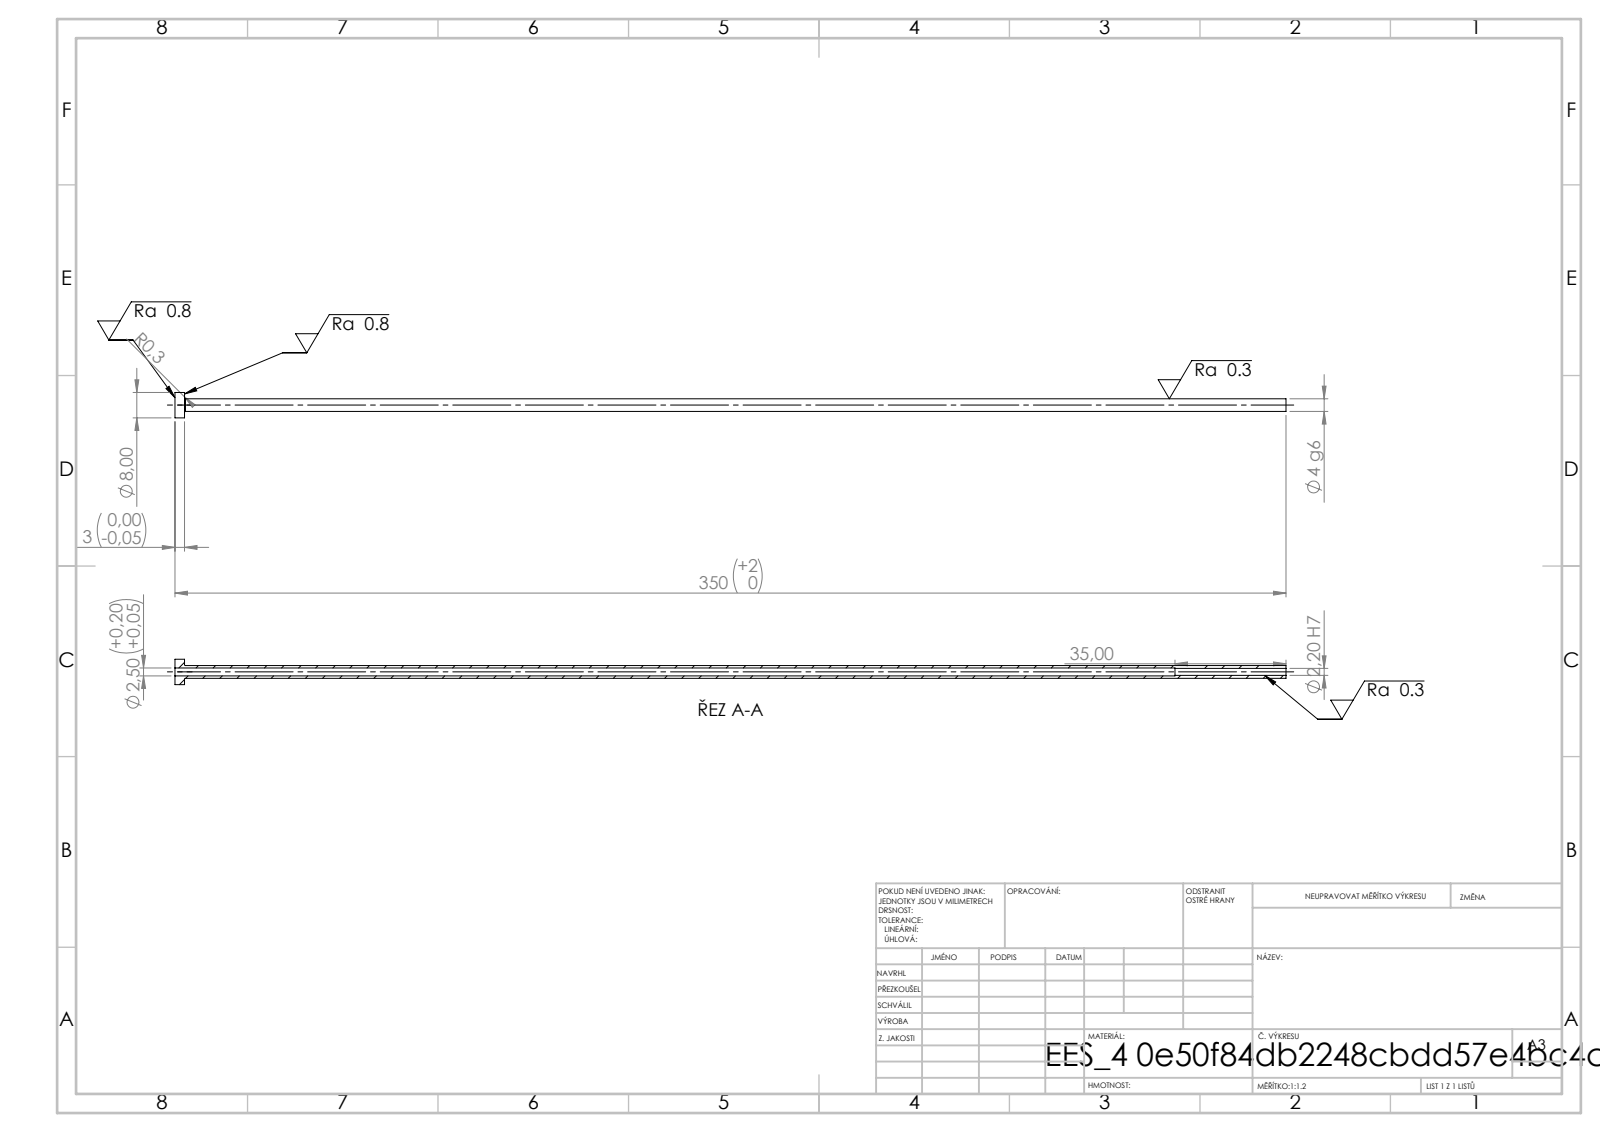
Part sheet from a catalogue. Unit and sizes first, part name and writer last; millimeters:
Units: millimetres
Overall size (bounding box): 350 × 8 × 8
Round holes (diameter × count): ⌀2.2 ×1, ⌀2.5 ×1
Round bosses / shafts (diameter × count): ⌀8 ×1, ⌀4 ×1
Main face-to-face distances: 3, 350, 347, 315, 312, 35
Volume: 2 832 mm³ · Surface area: 7 243 mm²
Bodies: 1 solid, 14 faces (4 planar, 8 cylindrical, 2 other)
STEP written by: SolidWorks 2019 (CONFIG_CONTROL_DESIGN)
